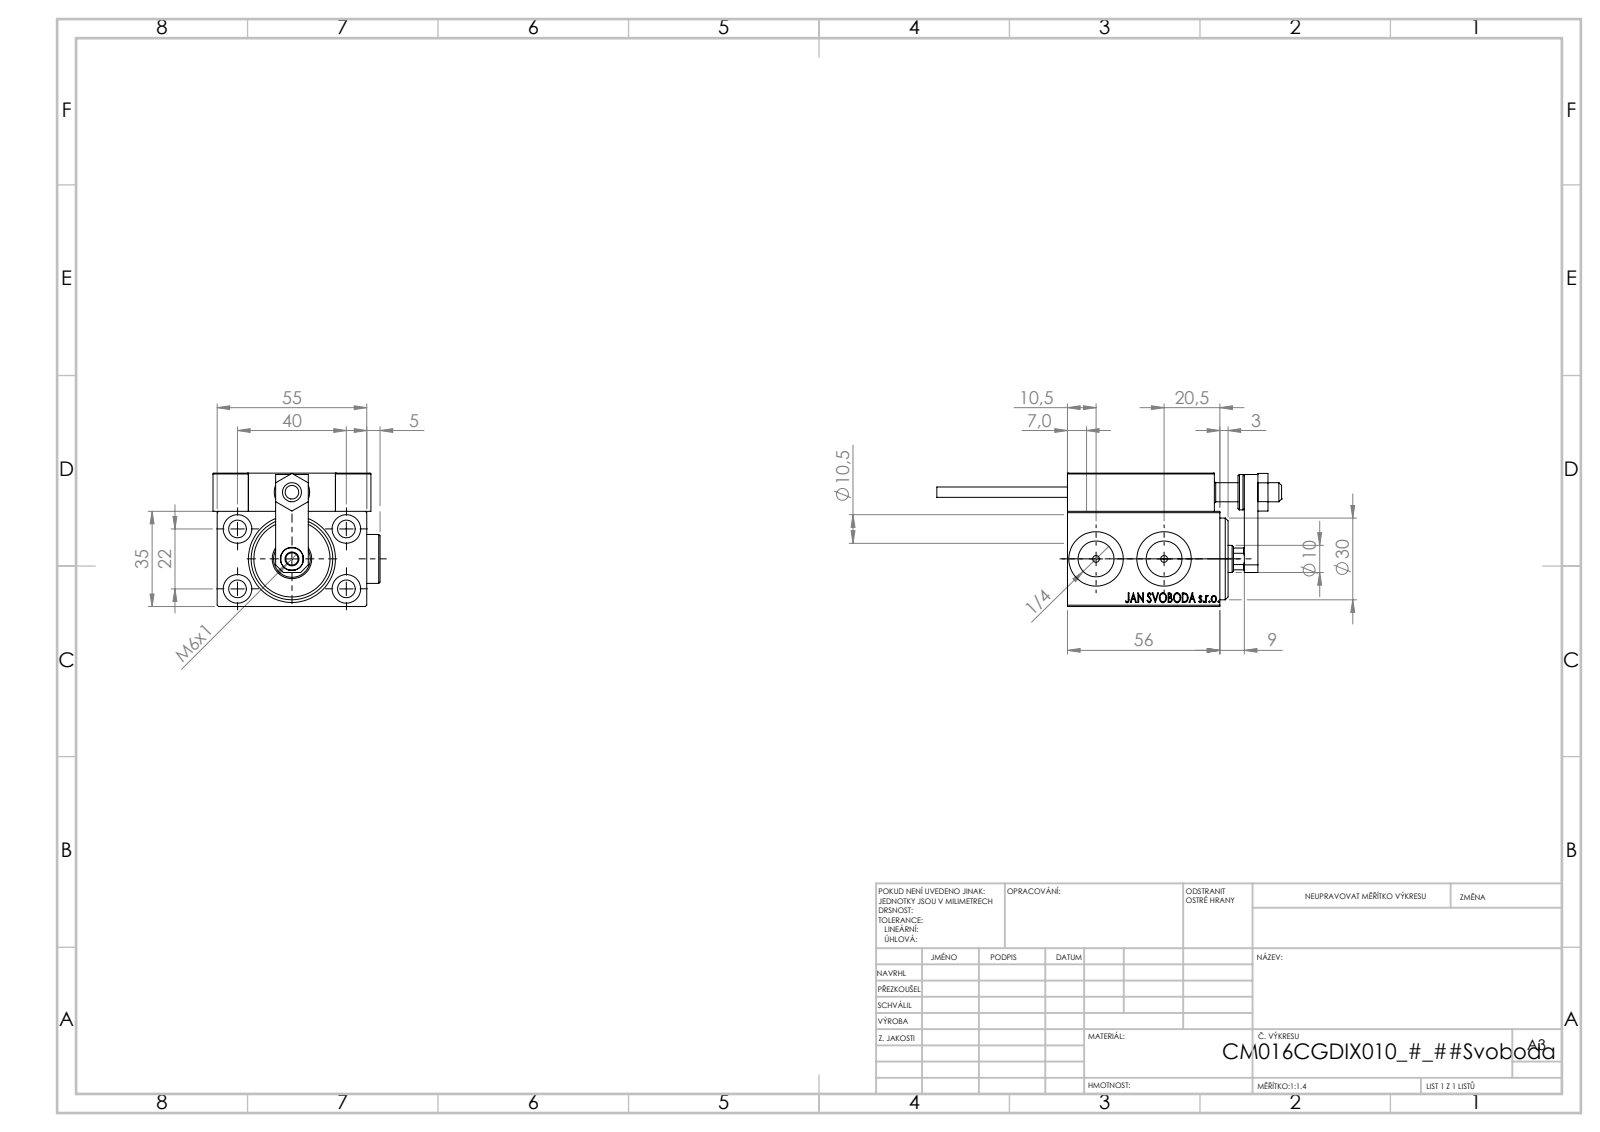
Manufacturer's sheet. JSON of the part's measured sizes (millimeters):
{"part_name": "ALLEN BOLT D5; TYC_L79; Zatka_OIL_PORT; NUT_D12 (+7 more)", "step_written_by": "SolidWorks 2019 (CONFIG_CONTROL_DESIGN)", "units": "millimeters", "bodies": {"solids": 25, "faces": 1339, "planar": 595, "cylindrical": 206, "other": 538}, "overall_size": [126.7, 61.4, 49], "volume_mm3": 134628, "surface_area_mm2": 52697, "round_holes": [[8, 5], [3.2, 4], [4, 4], [6.5, 4], [10.5, 4], [2.5, 2], [5, 2], [13.16, 2], [20, 2], [4.5, 1], [7, 1], [8.5, 1]], "round_bosses_or_shafts": [[18, 2], [5, 2], [3.8, 2], [13, 1], [11, 1]], "partial_cylinders_radius": [[0.3, 26], [3, 2], [4.5, 1]], "face_to_face_distances": [49, 35, 5, 14, 3, 7, 10, 1.5, 44, 55], "hole_center_spacings": [22.83, 8.25, 11.37, 20, 22, 23.41, 24.13, 29.59]}
